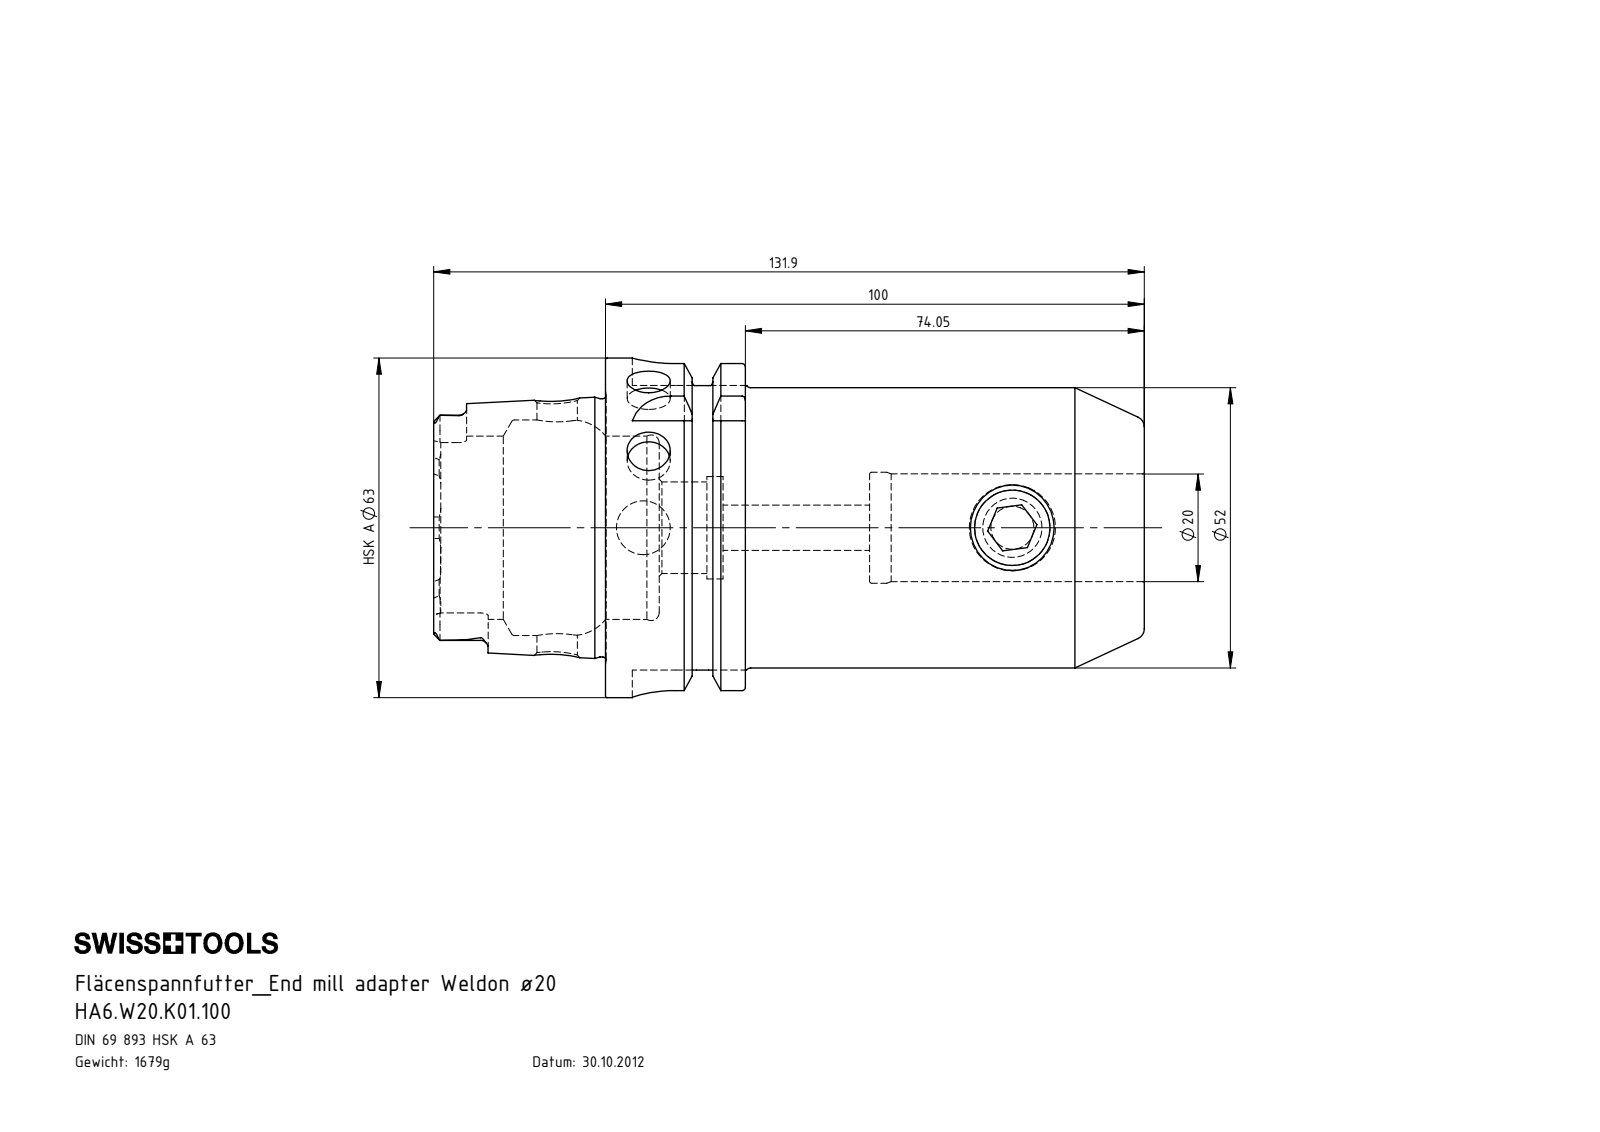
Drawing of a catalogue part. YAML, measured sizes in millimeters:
part_name: "HA6-W20.K01.100; W20-ER1.001.016; HA6-W20.K01.100_A_Fertigbearbeitung"
step_written_by: "SolidWorks 2012 (CONFIG_CONTROL_DESIGN)"
units: millimeters
bodies: {solids: 2, faces: 209, planar: 59, cylindrical: 57, other: 93}
overall_size: [131.9, 63, 63]
volume: 213918
surface_area: 39280
round_holes:
  - {diameter: 8, count: 2}
  - {diameter: 7.5, count: 1}
  - {diameter: 8.4, count: 1}
  - {diameter: 10, count: 1}
  - {diameter: 14, count: 1}
  - {diameter: 17, count: 1}
  - {diameter: 19, count: 1}
  - {diameter: 20, count: 1}
  - {diameter: 20.6, count: 1}
  - {diameter: 34, count: 1}
  - {diameter: 40, count: 1}
round_bosses_or_shafts:
  - {diameter: 63, count: 1}
  - {diameter: 54.95, count: 1}
  - {diameter: 52, count: 1}
  - {diameter: 47.94, count: 1}
  - {diameter: 16, count: 1}
partial_cylinders:
  - {radius: 1.4, count: 6}
  - {radius: 2.88, count: 4}
  - {radius: 8, count: 4}
face_to_face_distances: [100, 25.95, 74.05, 16, 9.95, 90.05, 31.9, 41.85, 57.85, 131.9]
hole_center_spacings: [68.5]
